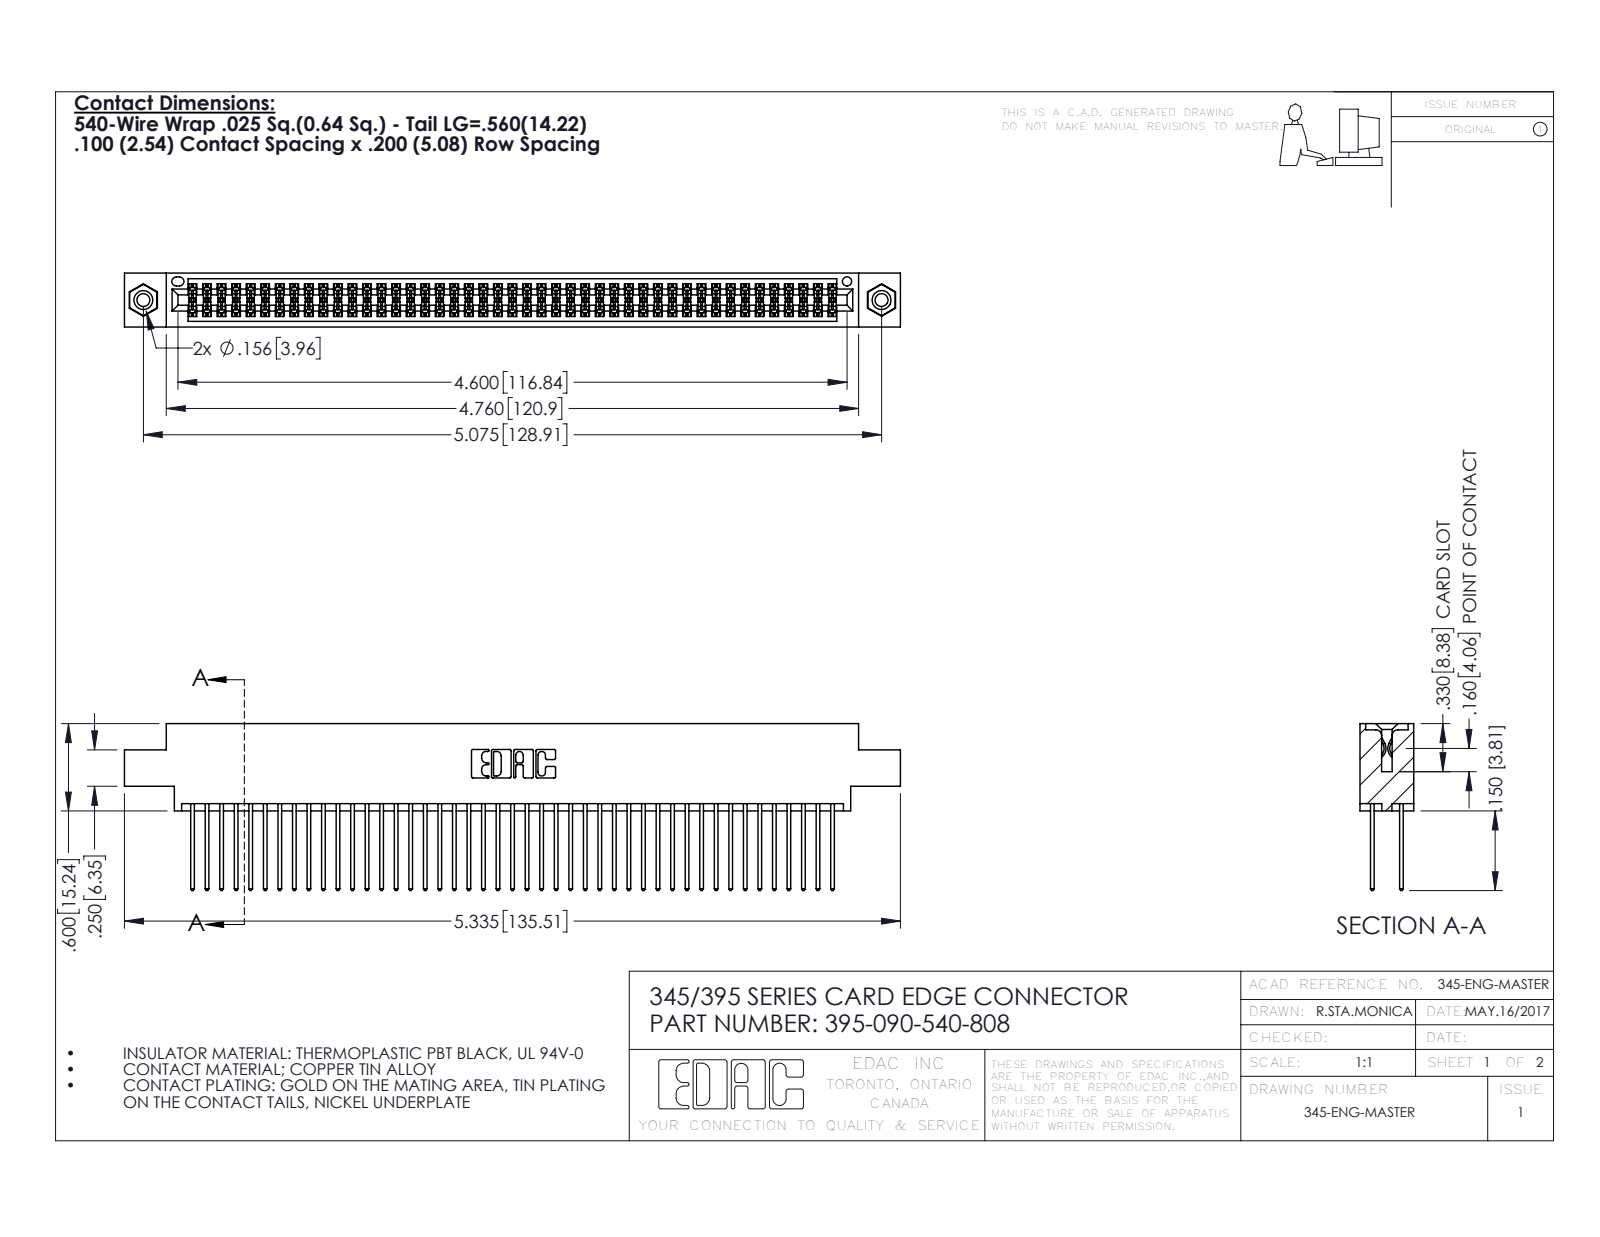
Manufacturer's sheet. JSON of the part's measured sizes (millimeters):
{"part_name": "345 Part_0.170 Offset - 0.156 Dia-TI; 345-292-001_345-293-140; 395-090-540-808; 345-250-001_345-250-003-102", "step_written_by": "SolidWorks 2016 (CONFIG_CONTROL_DESIGN)", "units": "millimeters", "bodies": {"solids": 93, "faces": 4690, "planar": 3086, "cylindrical": 1588, "other": 16}, "overall_size": [135.5, 29.1, 9.4], "volume_mm3": 13400, "surface_area_mm2": 21630, "round_holes": [[2.3, 2], [3.2, 2], [4, 2], [1.6, 1]], "round_bosses_or_shafts": [[3.9, 2]], "partial_cylinders_radius": [[0.2, 135], [0.3, 90], [0.3, 22], [0.2, 6], [0.8, 6], [0.7, 3], [0.4, 2], [0.5, 2]], "face_to_face_distances": [1.8, 7.6, 5.1, 2.5, 6.9, 0.6, 9.4, 5.7, 4.4, 3.8], "hole_center_spacings": [6.9, 122.9, 128.9]}
